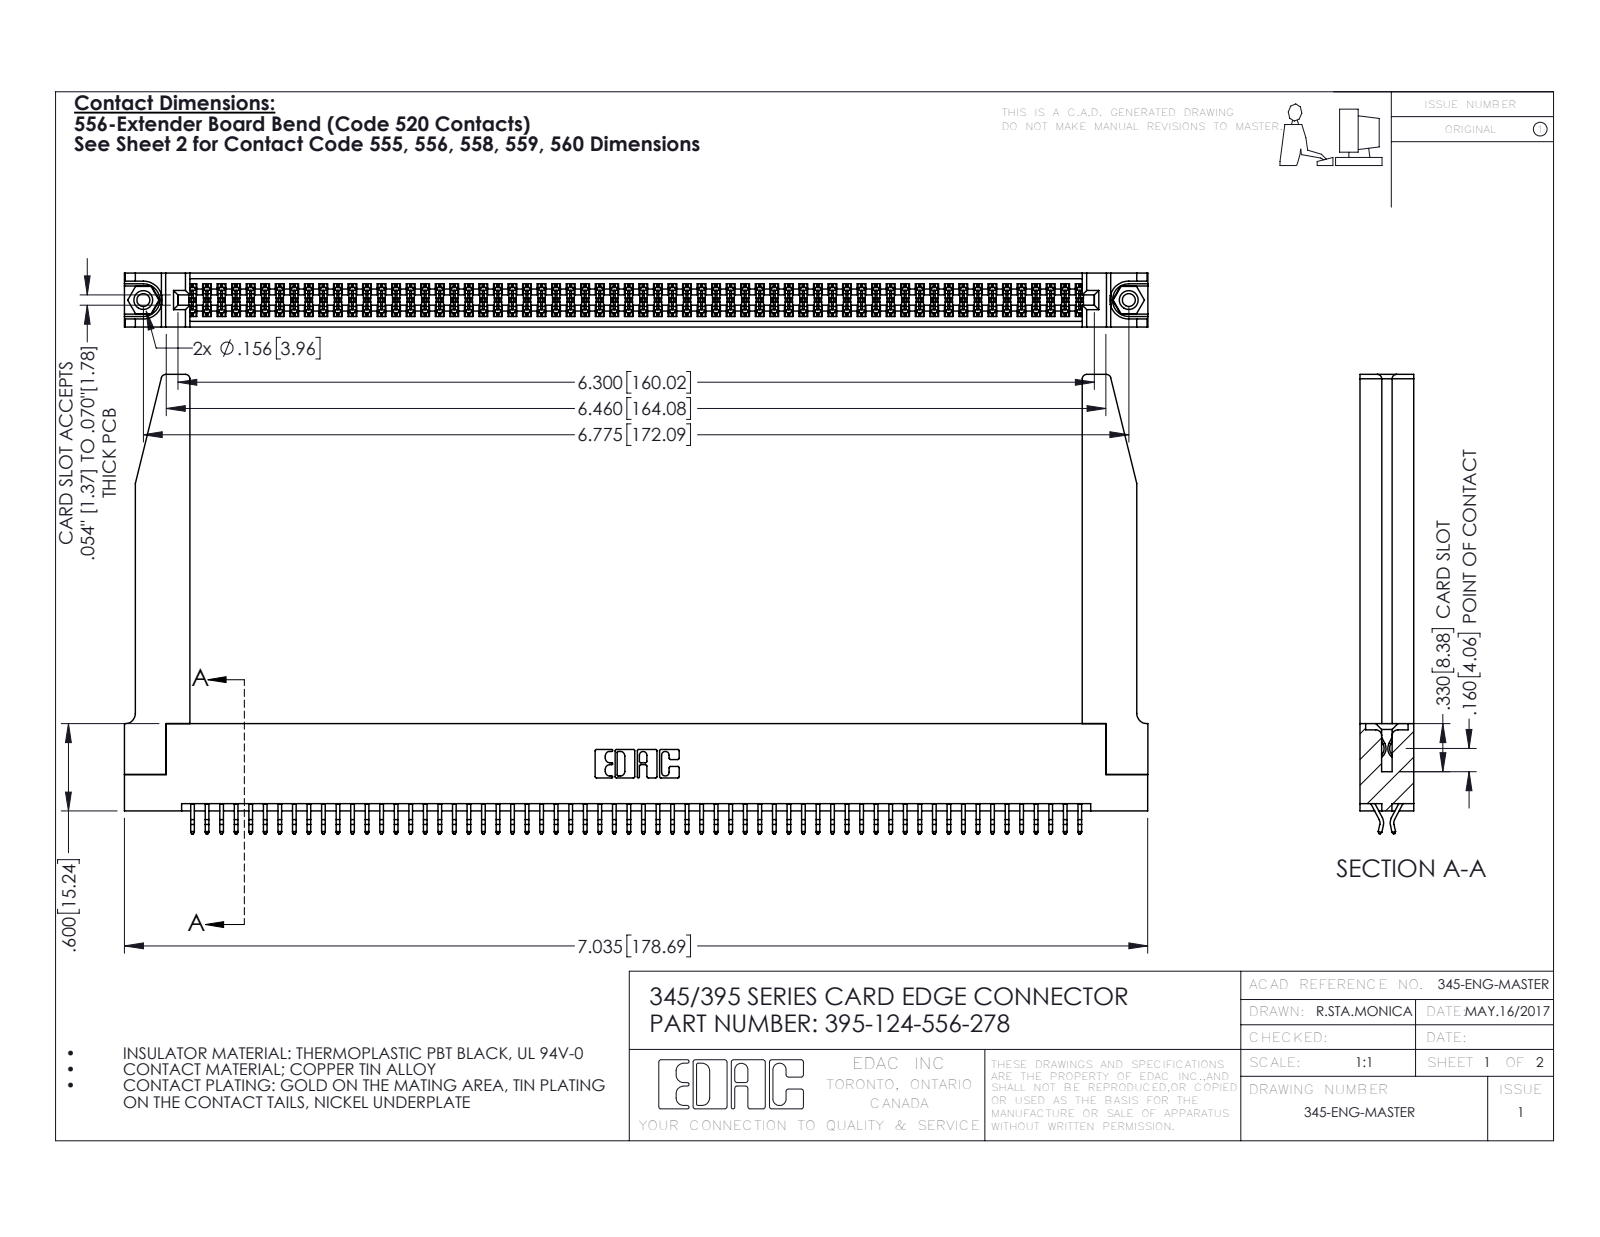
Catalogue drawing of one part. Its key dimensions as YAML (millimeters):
part_name: "345-250-001_345-250-001-102; 345-292-001_556 Tail; 345 Part_Flush Mounting Lugs - 0.156 Dia-TH; 345-220-078_345-220-078 (+1 more)"
step_written_by: "SolidWorks 2016 (CONFIG_CONTROL_DESIGN)"
units: millimeters
bodies: {solids: 129, faces: 7304, planar: 4810, cylindrical: 2442, other: 52}
overall_size: [178.7, 80.2, 9.4]
volume: 25320
surface_area: 33050
round_holes:
  - {diameter: 2.3, count: 2}
  - {diameter: 3.2, count: 2}
  - {diameter: 4, count: 2}
  - {diameter: 1.6, count: 1}
round_bosses_or_shafts:
  - {diameter: 3.9, count: 2}
partial_cylinders:
  - {radius: 0.2, count: 186}
  - {radius: 0.3, count: 22}
  - {radius: 0.8, count: 8}
  - {radius: 0.2, count: 6}
  - {radius: 0.8, count: 6}
  - {radius: 0.7, count: 3}
  - {radius: 0.3, count: 2}
  - {radius: 0.4, count: 2}
face_to_face_distances: [1.8, 7.6, 9.4, 5.1, 0.6, 2.5, 6.9, 5.7, 4.4, 3.8]
hole_center_spacings: [6.9, 166.1, 172.1]
